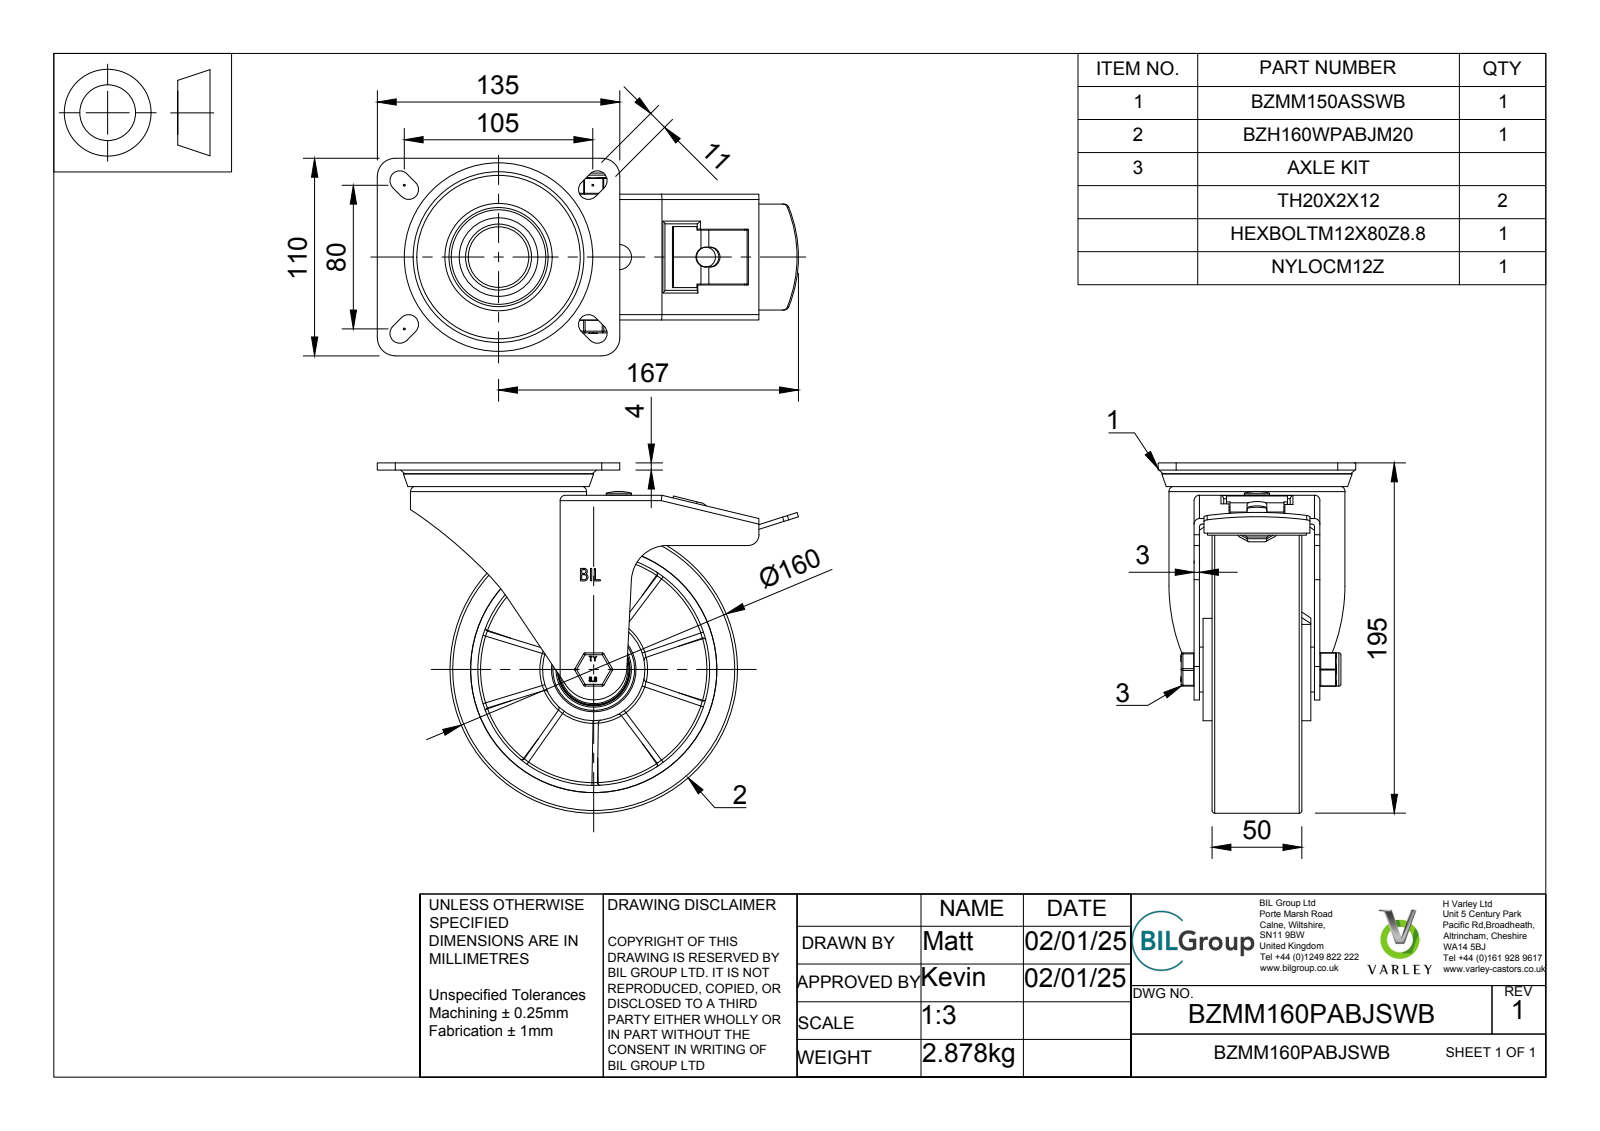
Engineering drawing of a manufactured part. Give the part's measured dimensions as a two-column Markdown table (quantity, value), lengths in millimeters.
| quantity | value |
| --- | --- |
| part name | BZMM160PABJSWB v3; BZMM150ASSWB - 64 v1; ZINC PLATED, PRESSED STEEL TOP PLATE; ZINC PLATED, PRESSED STEEL TOP PLATE Geometry (+7 more) |
| STEP written by | Autodesk Translation Framework v13.20.0.188 (AP242_MANAGED_MODEL_BASED_3D_ENGINEERING_MIM_LF) |
| units | millimeters |
| bodies | 82 solids, 1066 faces (386 planar, 249 cylindrical, 431 other) |
| overall size | 234.5 × 195 × 110 |
| volume | 730 937 mm³ |
| surface area | 351 866 mm² |
| round holes (diameter × count) | 8 × 1, 11 × 1, 12 × 1, 12.2 × 1, 14 × 1, 20 × 1, 28.5 × 1, 29.5 × 1, 33.75 × 1, 39.75 × 1, 40.5 × 1, 42 × 1 |
| round bosses / shafts (diameter × count) | 160 × 1, 98 × 1, 78 × 1, 57 × 1, 50 × 1, 41.5 × 1, 30.5 × 1, 27 × 1 |
| partial cylindrical surfaces (radius × count) | 0.5 × 18, 1 × 12, 1.5 × 10, 5.5 × 10, 0.25 × 6, 2.5 × 6, 3 × 6, 10 × 4 |
| main face-to-face distances | 3, 18, 5, 7, 9, 49, 8, 21, 4, 15 |
| hole center spacings | 67 |
